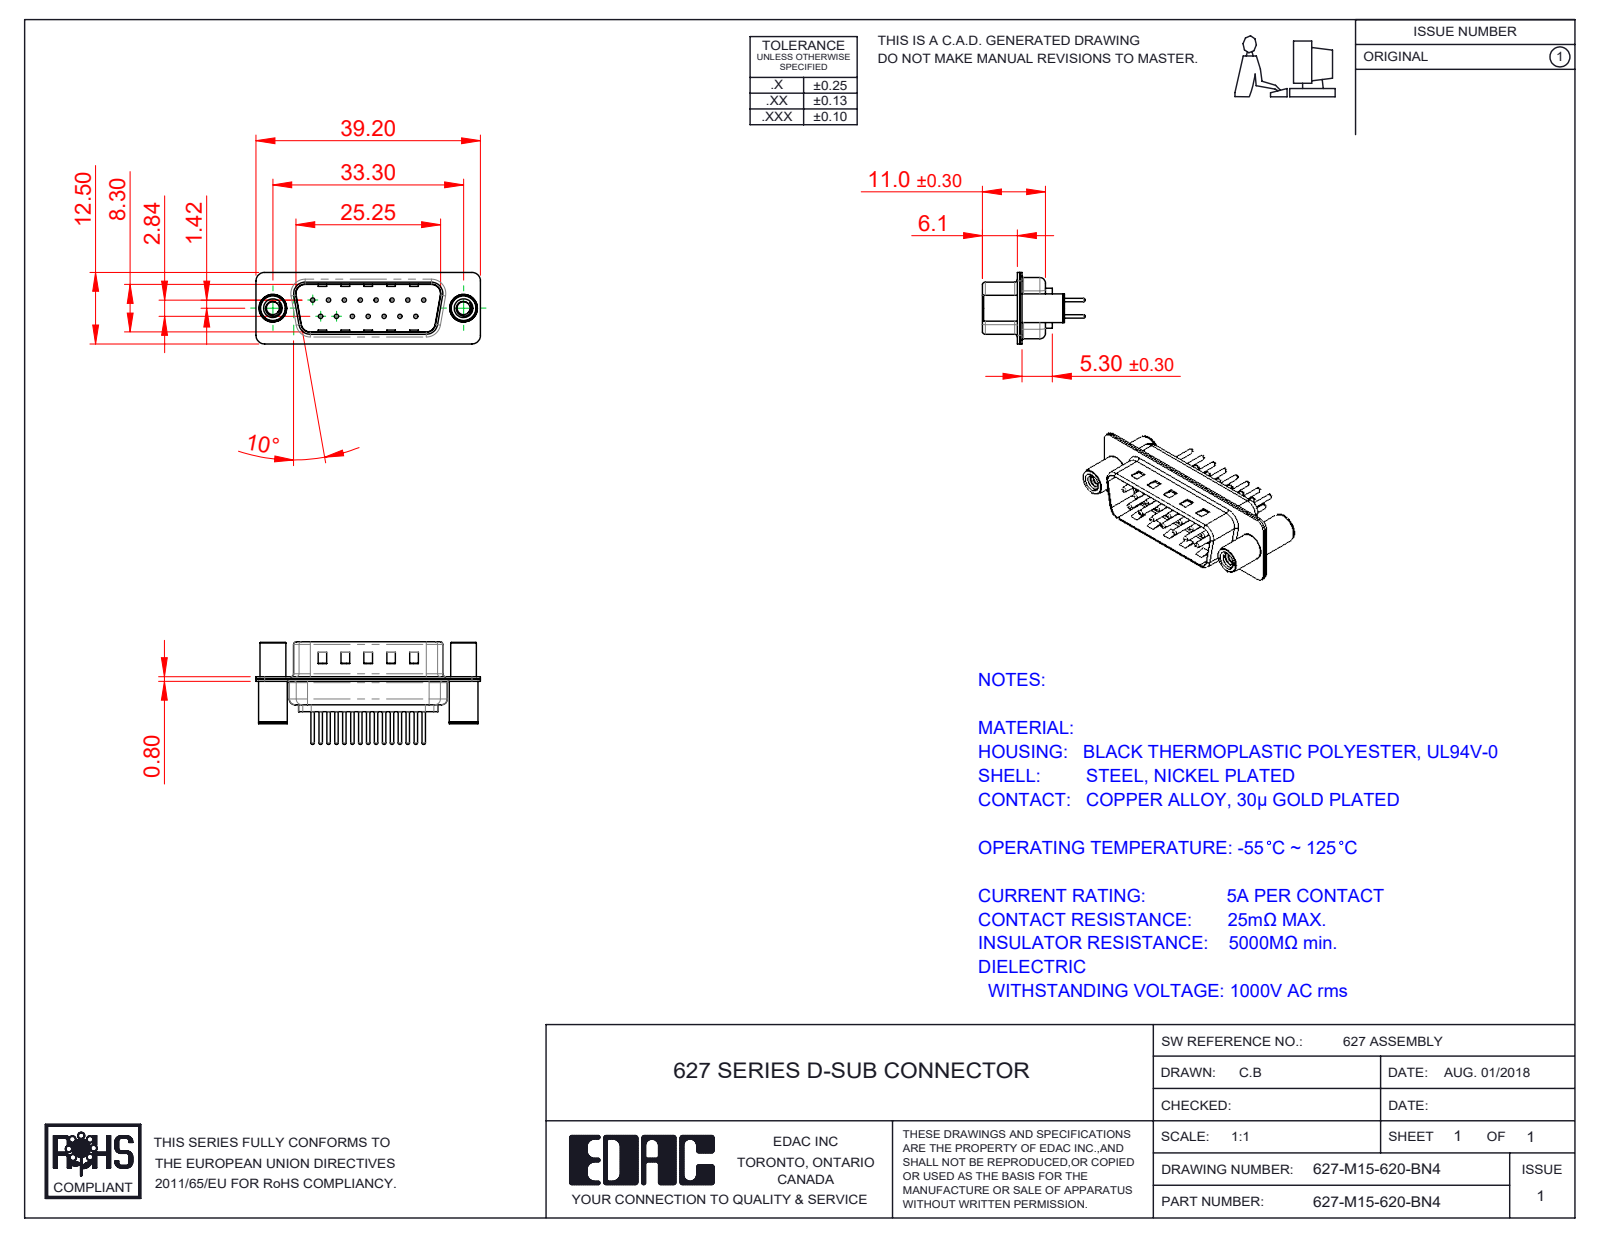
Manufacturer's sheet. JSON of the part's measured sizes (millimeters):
{"part_name": "627M Shell Front_15 Contacts; 627M 4-40 Threaded Standoff and Board Spacer; 627M Contact Row 1_20; 627M Shell Rear_15 Contacts (+3 more)", "step_written_by": "SolidWorks 2020 (CONFIG_CONTROL_DESIGN)", "units": "millimeters", "bodies": {"solids": 20, "faces": 981, "planar": 250, "cylindrical": 395, "other": 336}, "overall_size": [39.2, 17.9, 12.5], "volume_mm3": 2130, "surface_area_mm2": 5337, "round_holes": [[0.75, 15], [1.6, 15], [2, 15], [2.26, 2], [3.26, 2], [4, 2], [4.8, 2]], "round_bosses_or_shafts": [[1.5, 15], [0.6, 15], [5, 2], [4.9, 2], [4.5, 2]], "partial_cylinders_radius": [[1.5, 16], [2, 12], [0.5, 8], [1.6, 8], [0.25, 4], [0.6, 4], [0.65, 4], [0.9, 4]], "face_to_face_distances": [0.4, 0.8, 9.5, 9.1, 8.7, 9.9, 1.2, 5.3, 6.1, 5.7], "hole_center_spacings": [3.16, 2.77, 5.54, 8.31, 11.08, 5.03, 5.04, 7.48]}
